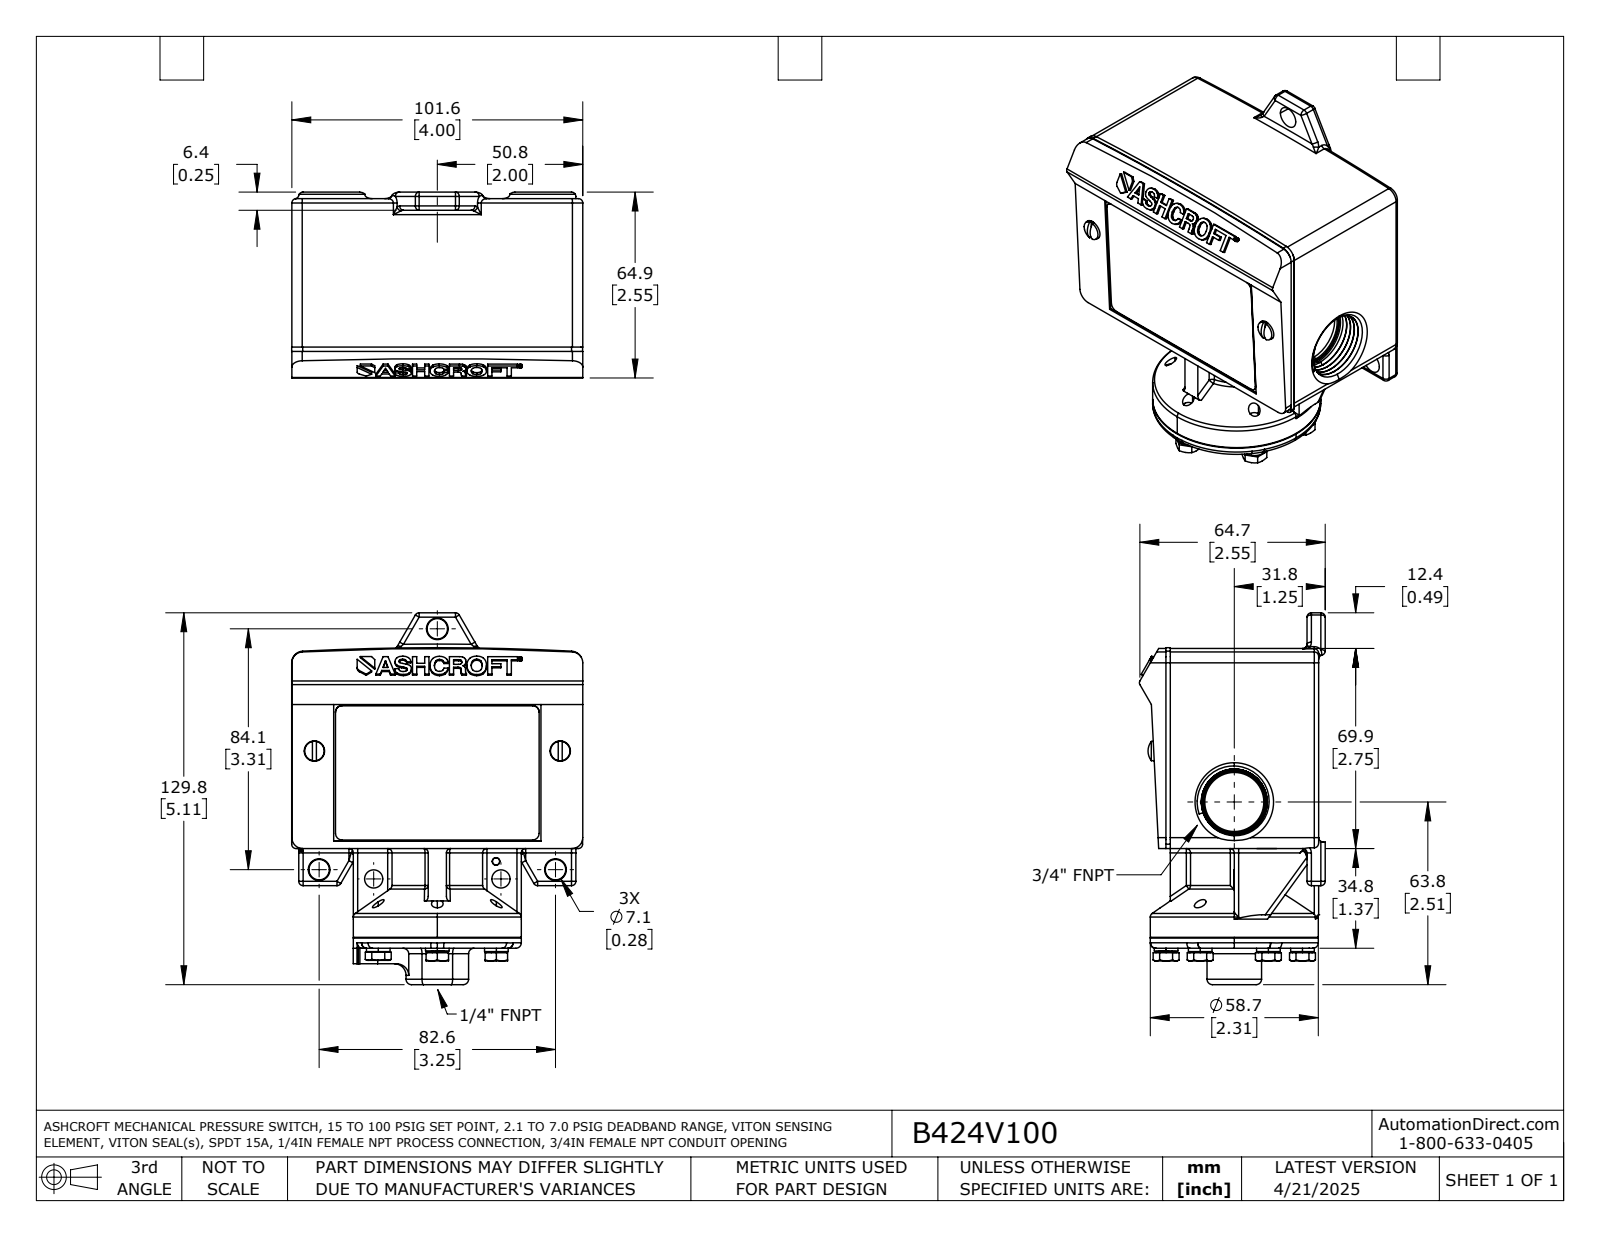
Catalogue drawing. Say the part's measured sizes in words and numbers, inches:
The part is named "B424V100". Its 3-D file was written by "SolidWorks 2021 (AUTOMOTIVE_DESIGN)". It is 2 solids with 1259 faces: 345 planar, 472 cylindrical and 442 other. Overall it measures 5.111 by 4.003 by 2.555 inches. Its volume is 28.57 cubic inches and its surface area 84.51 square inches. Round holes: 6 of diameter 0.161, 5 of diameter 0.192, 5 of diameter 0.209, 4 of diameter 0.187, 2 of diameter 0.28, 1 of diameter 0.455, 1 of diameter 0.812. Round bosses or shafts: 6 of diameter 0.325, 6 of diameter 0.278, 5 of diameter 0.19, 2 of diameter 0.27, 2 of diameter 0.25, 1 of diameter 2.31. Partial cylindrical surfaces (rounded edges, fillets, slot ends): 92 of radius 0.06, 5 of radius 0.03, 4 of radius 0.075, 4 of radius 0.09, 4 of radius 0.15, 2 of radius 0.01, 2 of radius 0.094, 2 of radius 0.16. The main face-to-face distances are 4, 0.015, 1.37, 0.09, 3.91, 0.44, 3.56, 3.47, 0.35, 0.845. The hole center spacings are 0.937, 1.624, 1.875, 0.938, 3.38.
